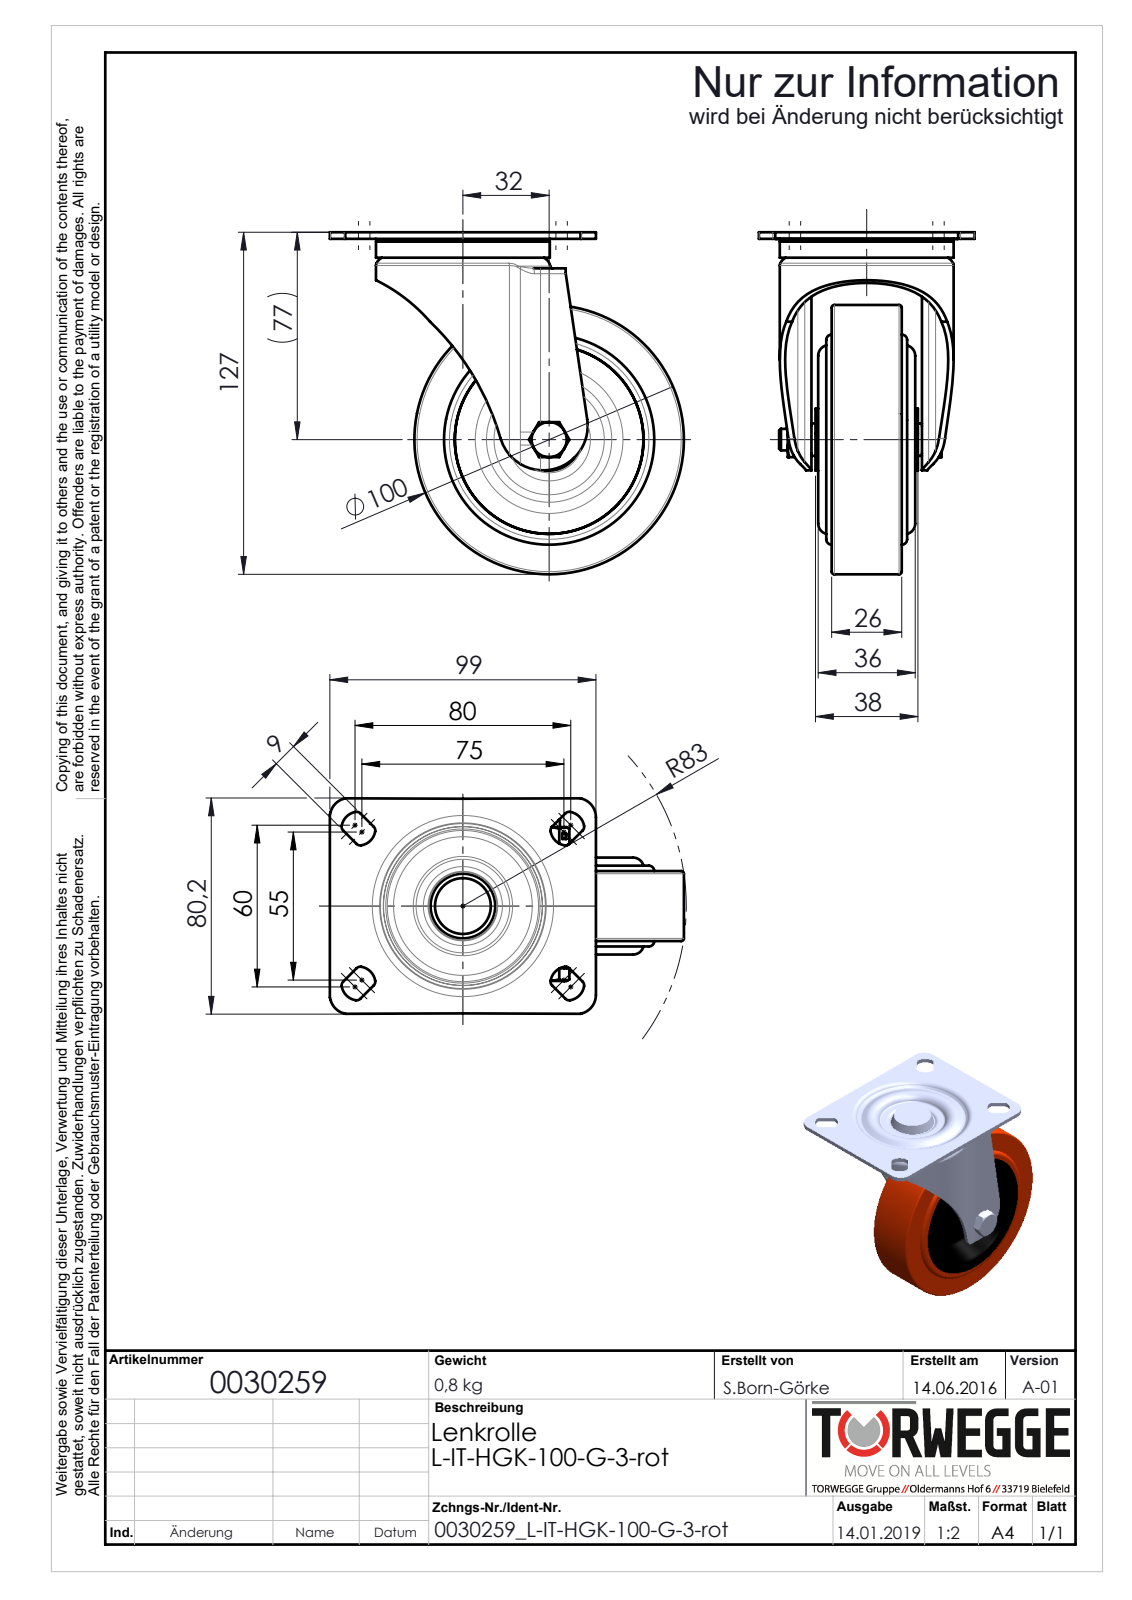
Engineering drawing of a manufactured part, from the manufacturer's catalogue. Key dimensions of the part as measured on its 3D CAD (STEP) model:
Part name (STEP PRODUCT): 0029403_BILOC_DIN934_M8_M8; 0030259_L-IT-HGK-100-G-3-rot_(A-01); K0016811_HGK-100-30-38-G12-rot; 0031045_IT-L-100-3-HT (+3 more)
STEP written by: SolidWorks 2018 (AUTOMOTIVE_DESIGN)
Units: millimetres
Bodies: 4 solids, 298 faces (90 planar, 89 cylindrical, 119 other)
Overall size (bounding box): 131.36 × 127 × 80
Volume: 6 666 mm³ · Surface area: 78 751 mm²
Round holes (diameter × count): ⌀6.8 ×1, ⌀8 ×1, ⌀8.39 ×1, ⌀10 ×1, ⌀12 ×1, ⌀13.5 ×1, ⌀13.6 ×1, ⌀36.4 ×1
Round bosses / shafts (diameter × count): ⌀13 ×2, ⌀100 ×1, ⌀67.26 ×1, ⌀64.5 ×1, ⌀58.15 ×1, ⌀24 ×1, ⌀9.99 ×1
Partial cylindrical surfaces — rounded edges, fillets, slot ends (radius × count): R2 ×18, R6.3 ×4, R7.12 ×4, R14 ×2, R16 ×2, R16.5 ×1, R30.25 ×1, R63.82 ×1
Main face-to-face distances: 2.45, 2, 35.5, 7.5, 26, 4.96, 7.41, 9.5, 43, 33.5
